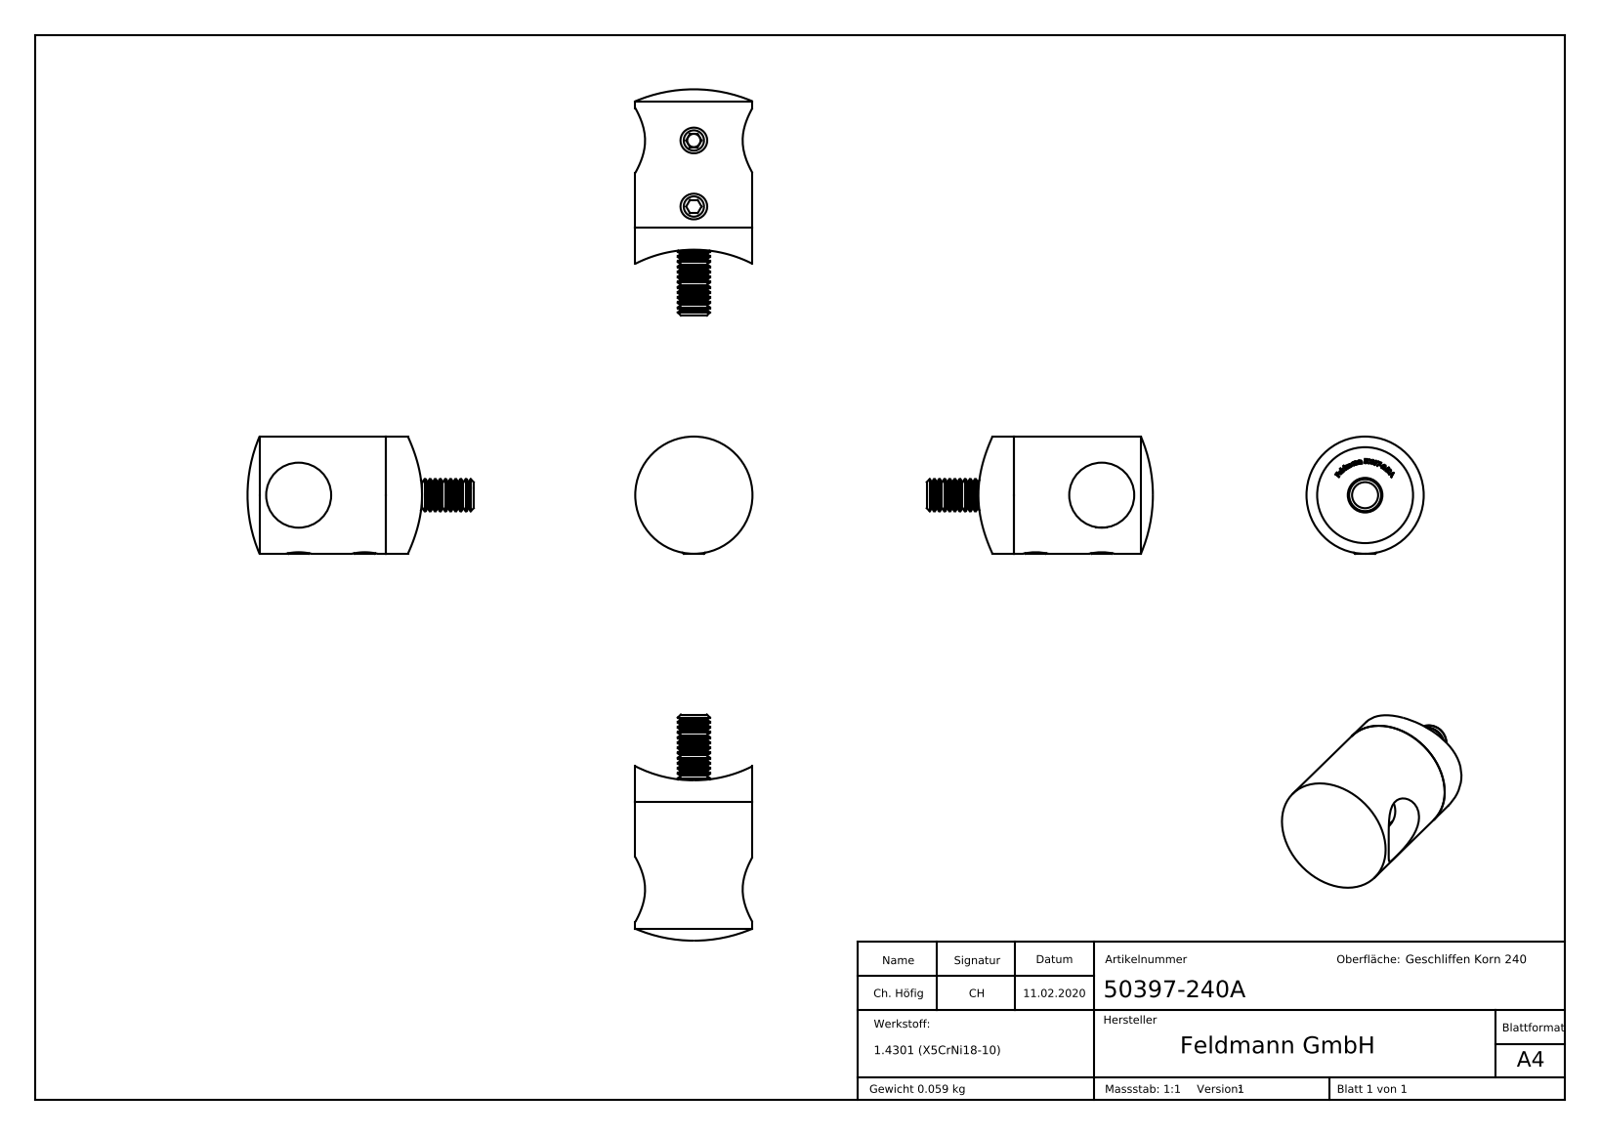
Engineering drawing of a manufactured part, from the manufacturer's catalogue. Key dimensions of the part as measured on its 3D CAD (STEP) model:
Part name (STEP PRODUCT): socket countersunk head screw_din_DIN 7991 - M6 x 25 --- 25S; socket countersunk head screw_din; Querstabhalter Teil1 Konfig_50XXX-240A Teil1 12,2; DIN913 (+7 more)
STEP written by: SolidWorks 2015 (CONFIG_CONTROL_DESIGN)
Units: millimetres
Bodies: 5 solids, 370 faces (173 planar, 36 cylindrical, 161 other)
Overall size (bounding box): 70 × 42.45 × 22
Volume: 8 100 mm³ · Surface area: 6 083 mm²
Round holes (diameter × count): ⌀4.2 ×2, ⌀6.5 ×1, ⌀12 ×1, ⌀12.2 ×1, ⌀18 ×1
Round bosses / shafts (diameter × count): ⌀5 ×2, ⌀22 ×1, ⌀11.9 ×1, ⌀11.57 ×1, ⌀6 ×1
Partial cylindrical surfaces — rounded edges, fillets, slot ends (radius × count): R24.15 ×1
Main face-to-face distances: 2.1, 10.65, 8.55, 2.5, 9.6, 7.5, 1.05, 14.35, 16.45, 23.95
Hole centre spacings: 12.4
